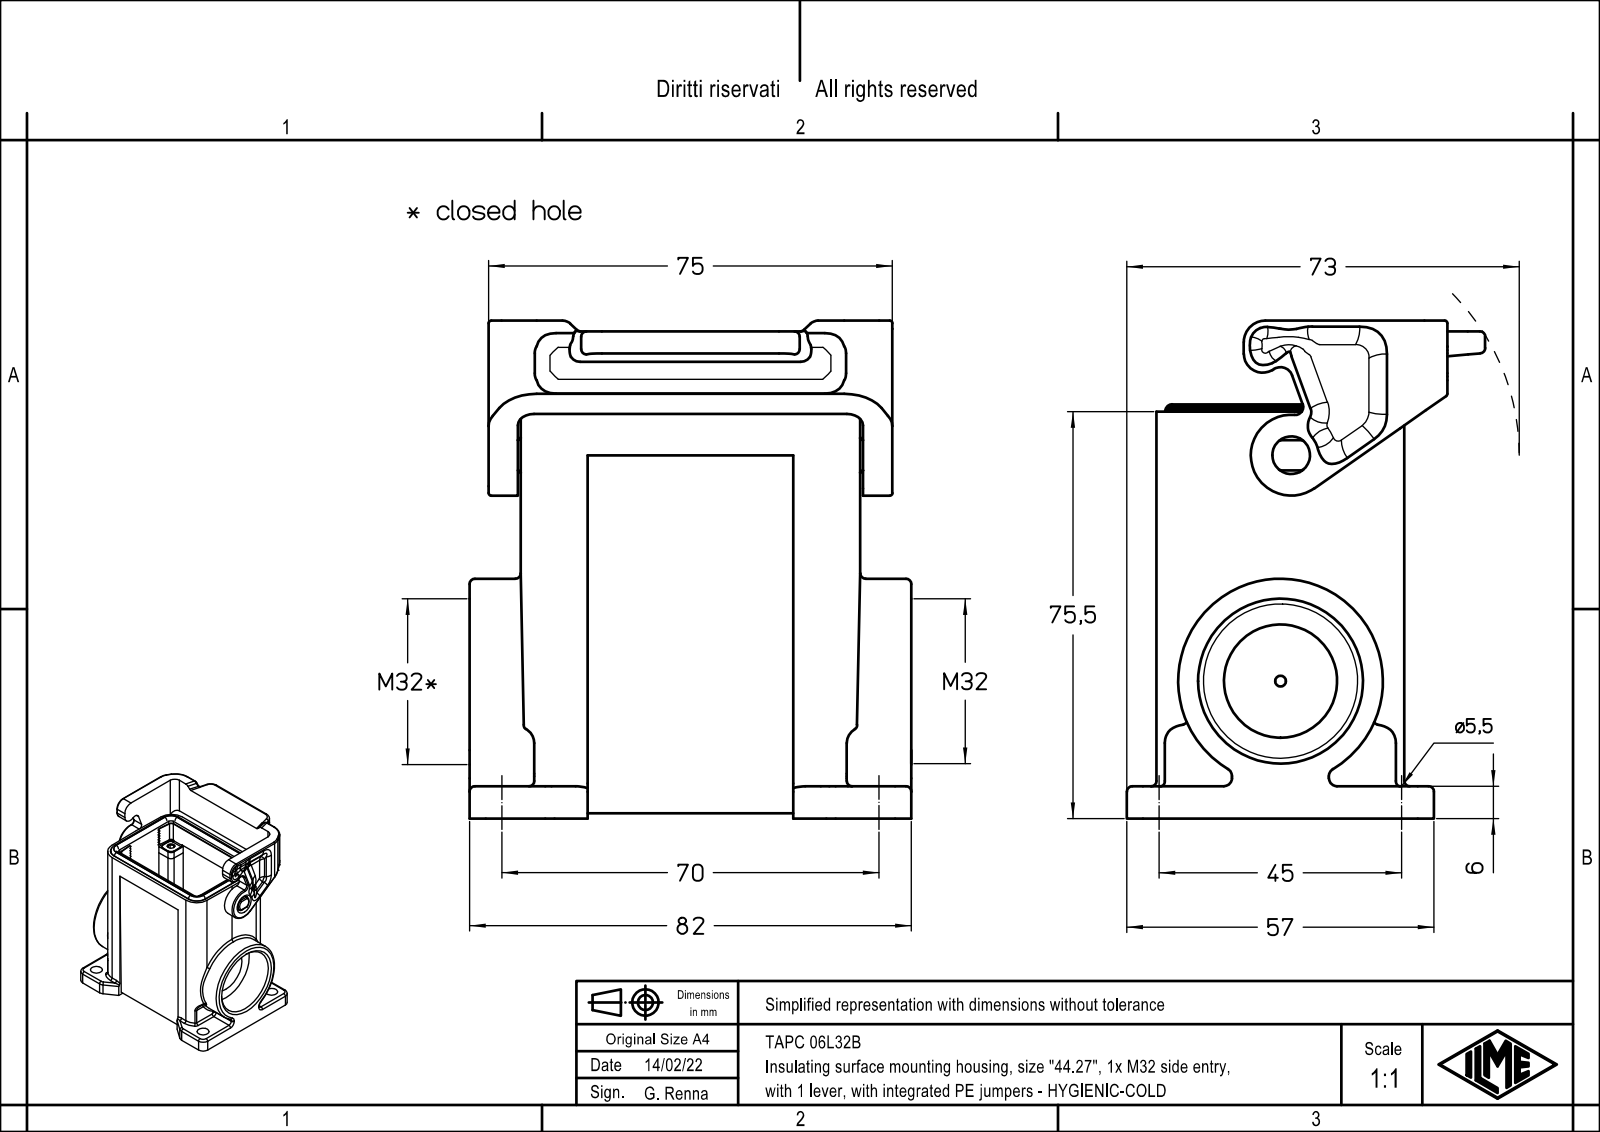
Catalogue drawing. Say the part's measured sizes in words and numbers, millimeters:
The part is named "TAPH 06 L32". Its 3-D file was written by "Creo Elements/Direct Modeling 20.1B 02-Apr-2019 (C) Parametric Technology GmbH (AUTOMOTIVE_DESIGN)". It is 1 solid with 518 faces: 314 planar, 168 cylindrical and 36 other. Overall it measures 92.4 by 82 by 66.5 millimeters. Its volume is 125 937 cubic millimeters and its surface area 50 441 square millimeters. Round holes: 4 of diameter 3.5, 4 of diameter 5.5, 1 of diameter 28, 1 of diameter 30.6. Round bosses or shafts: 1 of diameter 38. Partial cylindrical surfaces (rounded edges, fillets, slot ends): 17 of radius 1.5, 17 of radius 3, 14 of radius 2, 12 of radius 1.3, 8 of radius 1, 6 of radius 0.5, 4 of radius 1.6, 4 of radius 6. The main face-to-face distances are 46, 5.4, 40.6, 40.59, 35.19, 5.41, 5.5, 1, 14.9, 6.1. The hole center spacings are 15.81, 38.28, 57.71, 67.42, 27, 44, 45, 51.62.
